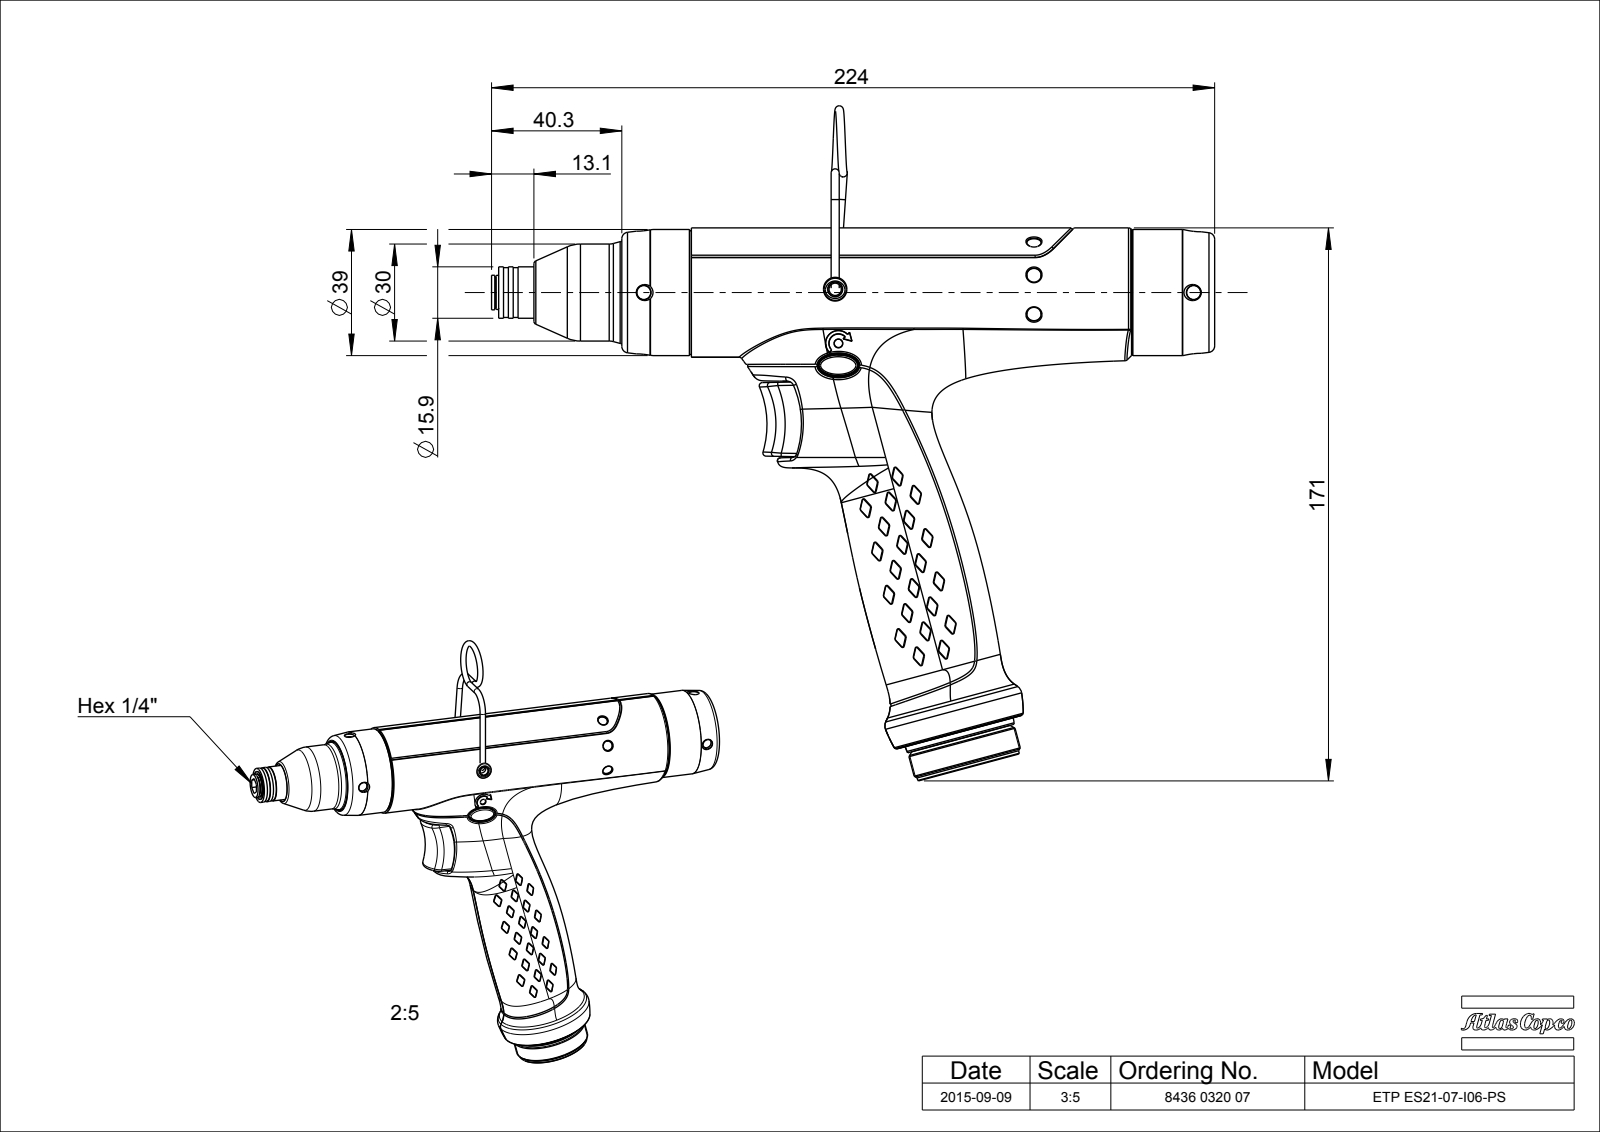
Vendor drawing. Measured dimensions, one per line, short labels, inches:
name: PRT0001
written by: CREO PARAMETRIC BY PTC INC, 2020281 (CONFIG_CONTROL_DESIGN)
unit: in
bodies: 2 solids, 966 faces (103 planar, 128 cylindrical, 735 other)
size: 8.807 × 6.732 × 1.717
volume: 23.62 in³; area: 75.93 in²
holes: 4× ⌀0.177, 1× ⌀0.071, 1× ⌀0.15, 1× ⌀1.154
bosses: 2× ⌀0.173, 1× ⌀1.575, 1× ⌀1.535, 1× ⌀1.339, 1× ⌀1.28, 1× ⌀1.24, 1× ⌀1.181, 1× ⌀0.626
rounds: 9× R0.039, 6× R0.011, 6× R0.02, 6× R0.089, 4× R0.016, 4× R0.02, 4× R0.047, 2× R0.008
face distances: 4.972, 0.941, 2.789, 1.848, 3.969, 1.004, 3.748, 7.717, 8.721, 7.693
hole spacings: 6.697, 0.926, 2.331, 2.448, 4.366, 4.502
